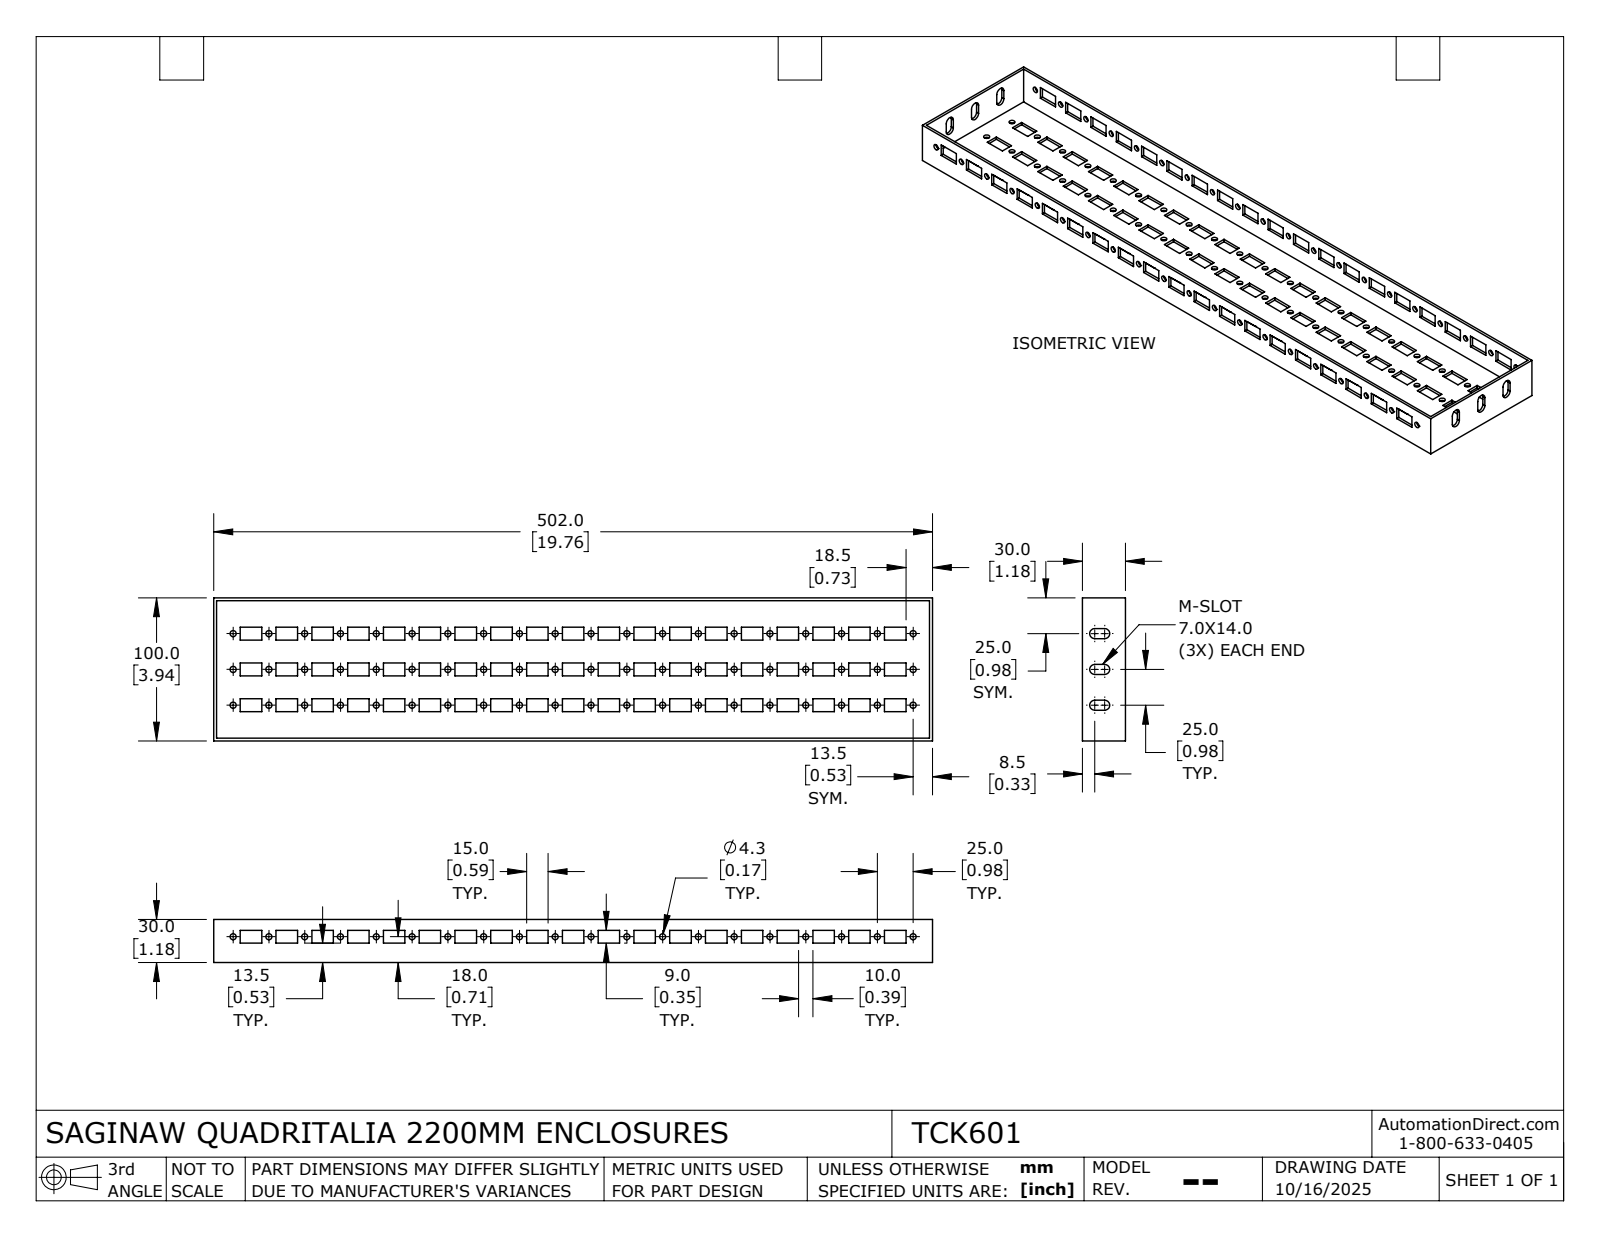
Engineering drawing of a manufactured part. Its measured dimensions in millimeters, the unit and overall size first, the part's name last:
Units: millimetres
Overall size (bounding box): 502 × 100 × 30
Round holes (diameter × count): ⌀4.25 ×80
Partial cylindrical surfaces — rounded edges, fillets, slot ends (radius × count): R3.5 ×6
Main face-to-face distances: 2, 98, 100, 96, 500, 25, 9, 502, 498, 30
Hole centre spacings: 25, 50, 55.9, 75, 35.36, 100, 125, 79.06
Volume: 137 839 mm³ · Surface area: 152 469 mm²
Bodies: 1 solid, 515 faces (403 planar, 112 cylindrical, 0 other)
Part name (STEP PRODUCT): TCK601
STEP written by: SolidWorks 2024 (AUTOMOTIVE_DESIGN)
